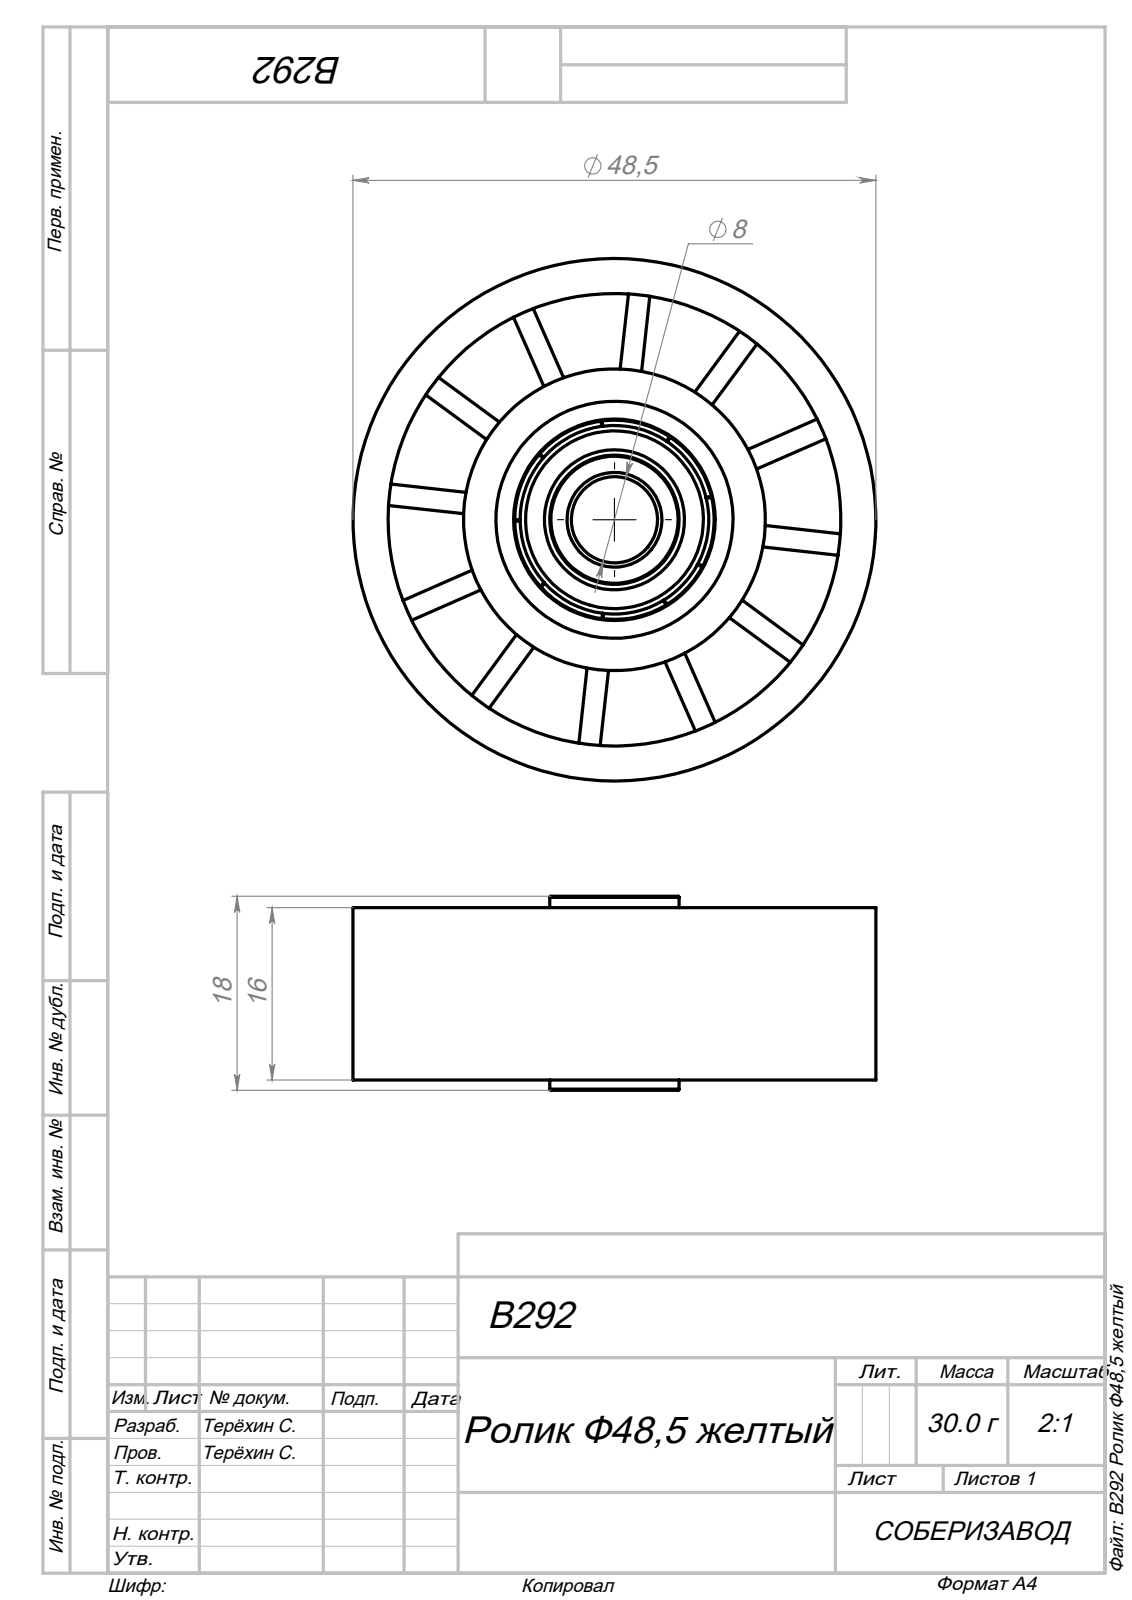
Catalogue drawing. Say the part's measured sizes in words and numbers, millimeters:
The part is named "B292 Ролик Ф48,5 желтый; Сборка1; B292- ролик; B292 -подшипник1 (+3 more)". Its 3-D file was written by "SolidWorks 2022 (AUTOMOTIVE_DESIGN)". It is 5 solids with 232 faces: 160 planar, 28 cylindrical and 44 other. Overall it measures 48.5 by 48.5 by 18 millimeters. Its volume is 16 407 cubic millimeters and its surface area 13 979 square millimeters. Round holes: 1 of diameter 8, 1 of diameter 12, 1 of diameter 17.5, 1 of diameter 18.5, 1 of diameter 22, 1 of diameter 42. Round bosses or shafts: 1 of diameter 48.5, 1 of diameter 28, 1 of diameter 25. The main face-to-face distances are 9, 3, 4, 7, 2, 12, 5, 13, 1, 6.
